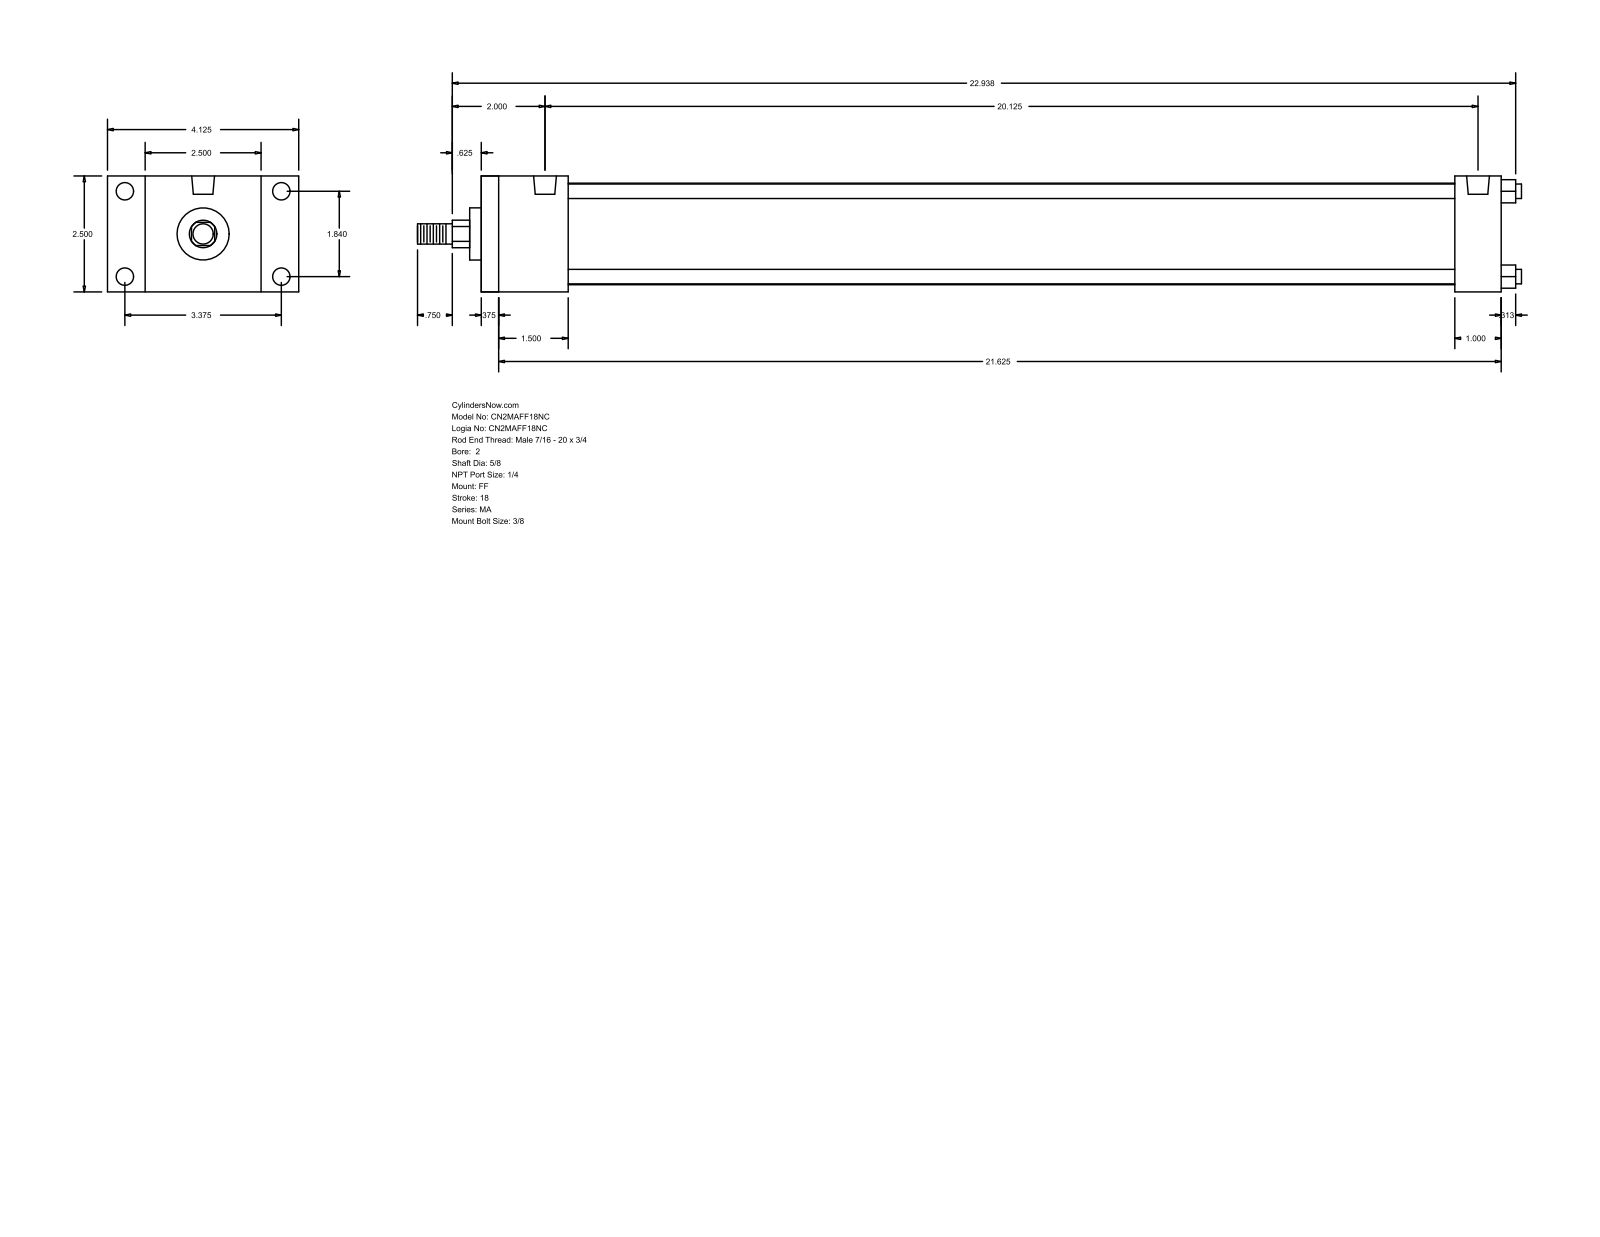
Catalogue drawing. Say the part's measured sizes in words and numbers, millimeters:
The part is named "MA_FF__0200_0.625". Its 3-D file was written by "GSSL Pune (CONFIG_CONTROL_DESIGN)". It is 0 solids with 92 faces: 64 planar, 28 cylindrical and 0 other. Overall it measures 604.84 by 104.78 by 63.5 millimeters. Round holes: 4 of diameter 7.94, 4 of diameter 9.53, 2 of diameter 12.49. Round bosses or shafts: 4 of diameter 7.94, 1 of diameter 55.63, 1 of diameter 28.57, 1 of diameter 15.88, 1 of diameter 11.11. Partial cylindrical surfaces (rounded edges, fillets, slot ends): 1 of radius 7.54. The main face-to-face distances are 63.5, 558.79, 549.27, 9.52, 25.4, 38.1, 47.62, 533.39, 523.87, 485.77. The hole center spacings are 46.74, 85.72, 97.63, 511.18.
